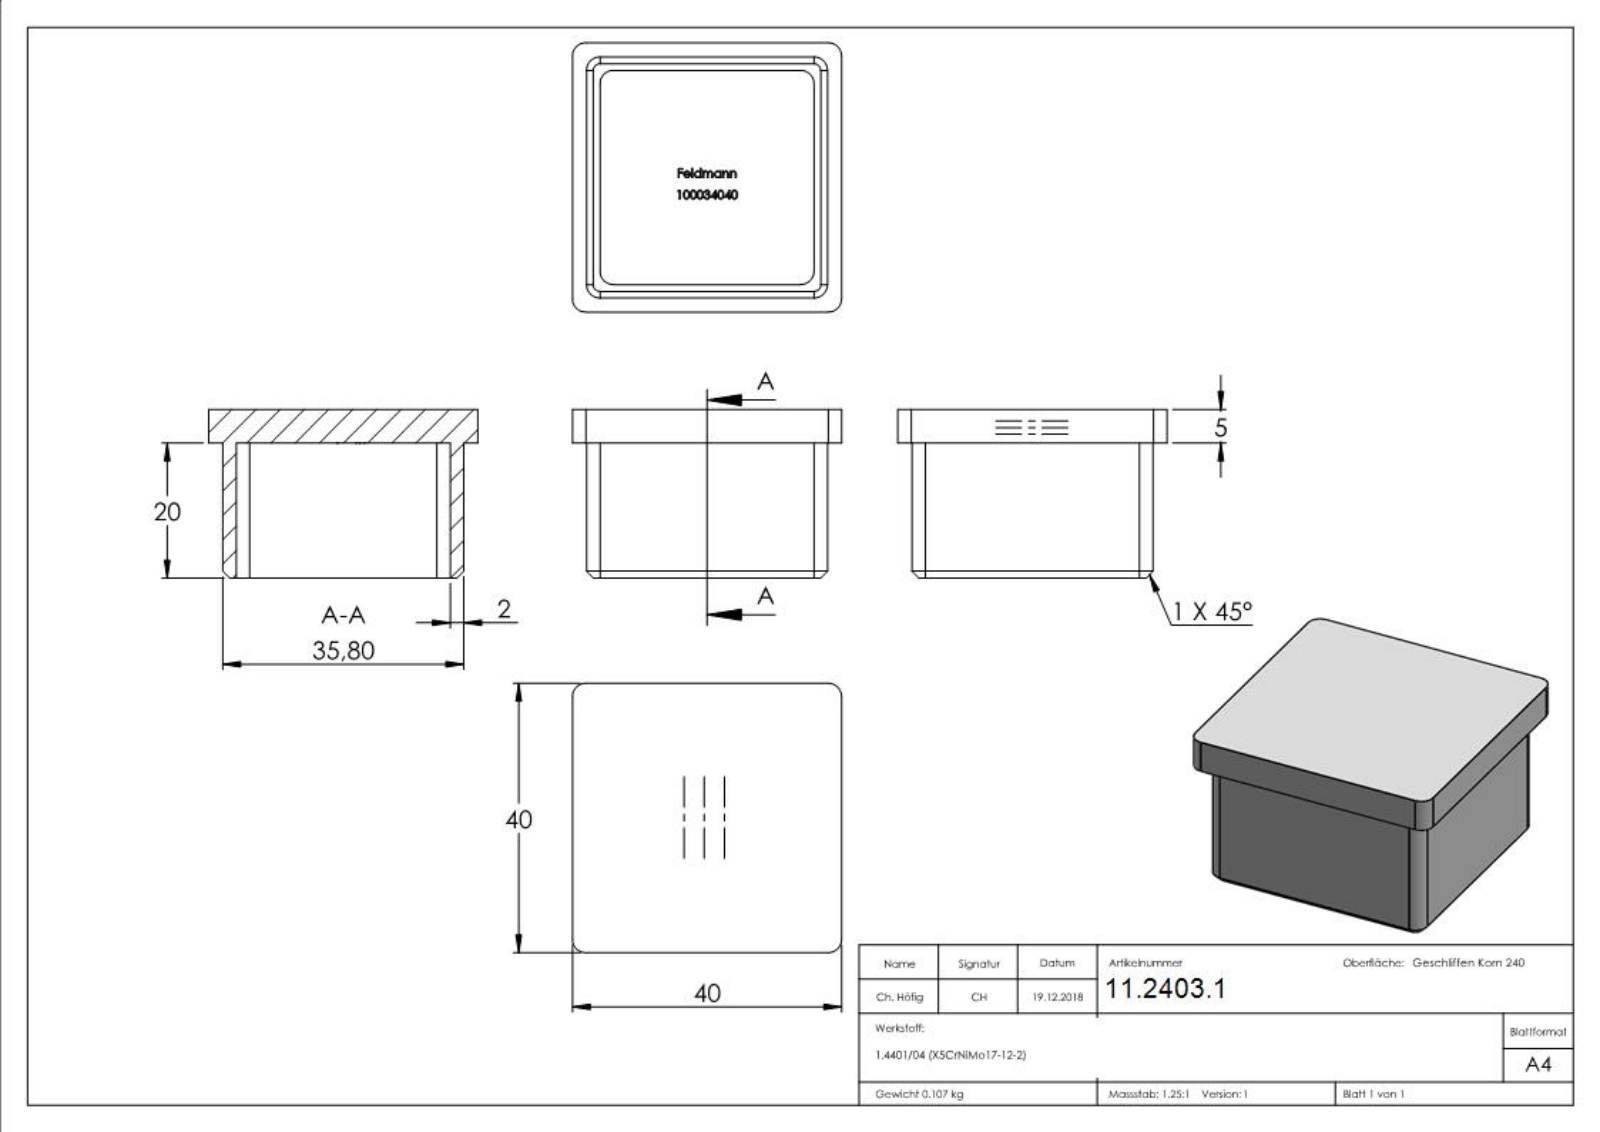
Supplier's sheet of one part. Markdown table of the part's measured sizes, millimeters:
| quantity | value |
| --- | --- |
| part name | 100034040 |
| STEP written by | SolidWorks 2015 (CONFIG_CONTROL_DESIGN) |
| units | millimeters |
| bodies | 1 solid, 259 faces (136 planar, 12 cylindrical, 111 other) |
| overall size | 40 × 40 × 25 |
| volume | 13 321 mm³ |
| surface area | 9 174 mm² |
| partial cylindrical surfaces (radius × count) | 2 × 12 |
| main face-to-face distances | 2, 33.8, 5, 35.8, 31.8, 2.1, 4.1, 35.9, 37.9, 40 |
